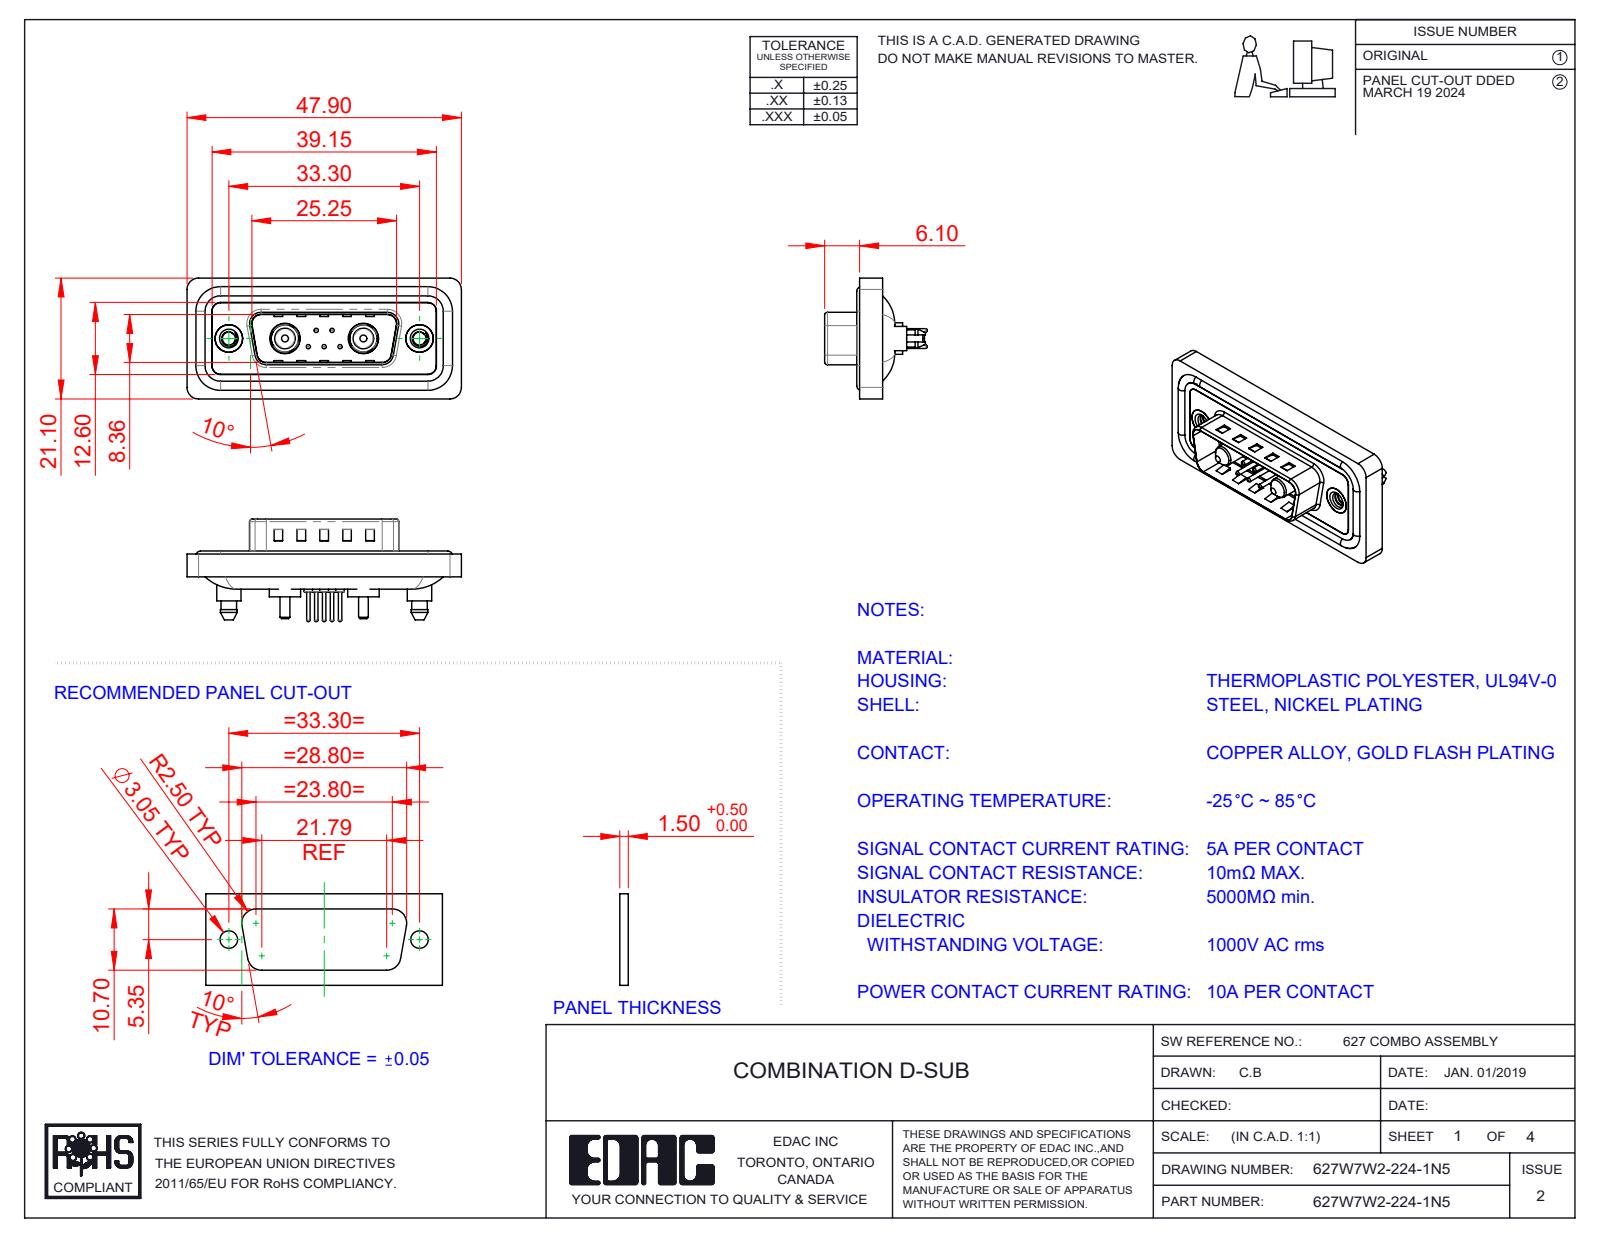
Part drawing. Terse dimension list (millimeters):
name: 627Combo Waterproof Housing_15 Contacts; 627Combo Shell Rear_15 Contacts; 627Combo Contact Row 1_24; Power Pin_10A S (+5 more)
written by: SolidWorks 2023 (CONFIG_CONTROL_DESIGN)
unit: mm
bodies: 16 solids, 760 faces (248 planar, 324 cylindrical, 188 other)
size: 47.9 × 21.1 × 17.9
volume: 5 621 mm³; area: 9 101 mm²
holes: 5× ⌀0.75, 5× ⌀1.6, 5× ⌀2, 2× ⌀2.26, 2× ⌀4, 2× ⌀4.8, 2× ⌀4.85, 2× ⌀5, 2× ⌀5.3
bosses: 5× ⌀1.5, 5× ⌀0.6, 4× ⌀1.6, 2× ⌀5.5, 2× ⌀5.4, 2× ⌀5.2, 2× ⌀4.9, 2× ⌀4.75
rounds: 28× R1.5, 20× R2, 10× R1.6, 8× R0.5, 4× R0.25, 4× R0.6, 4× R0.65, 4× R0.9
face distances: 0.4, 1.1, 1.5, 1.6, 0.5, 3.1, 2.9, 4, 0.7, 0.82
hole spacings: 3.16, 2.77, 9.8, 23.5, 4.31, 4.33, 5.03, 5.04
